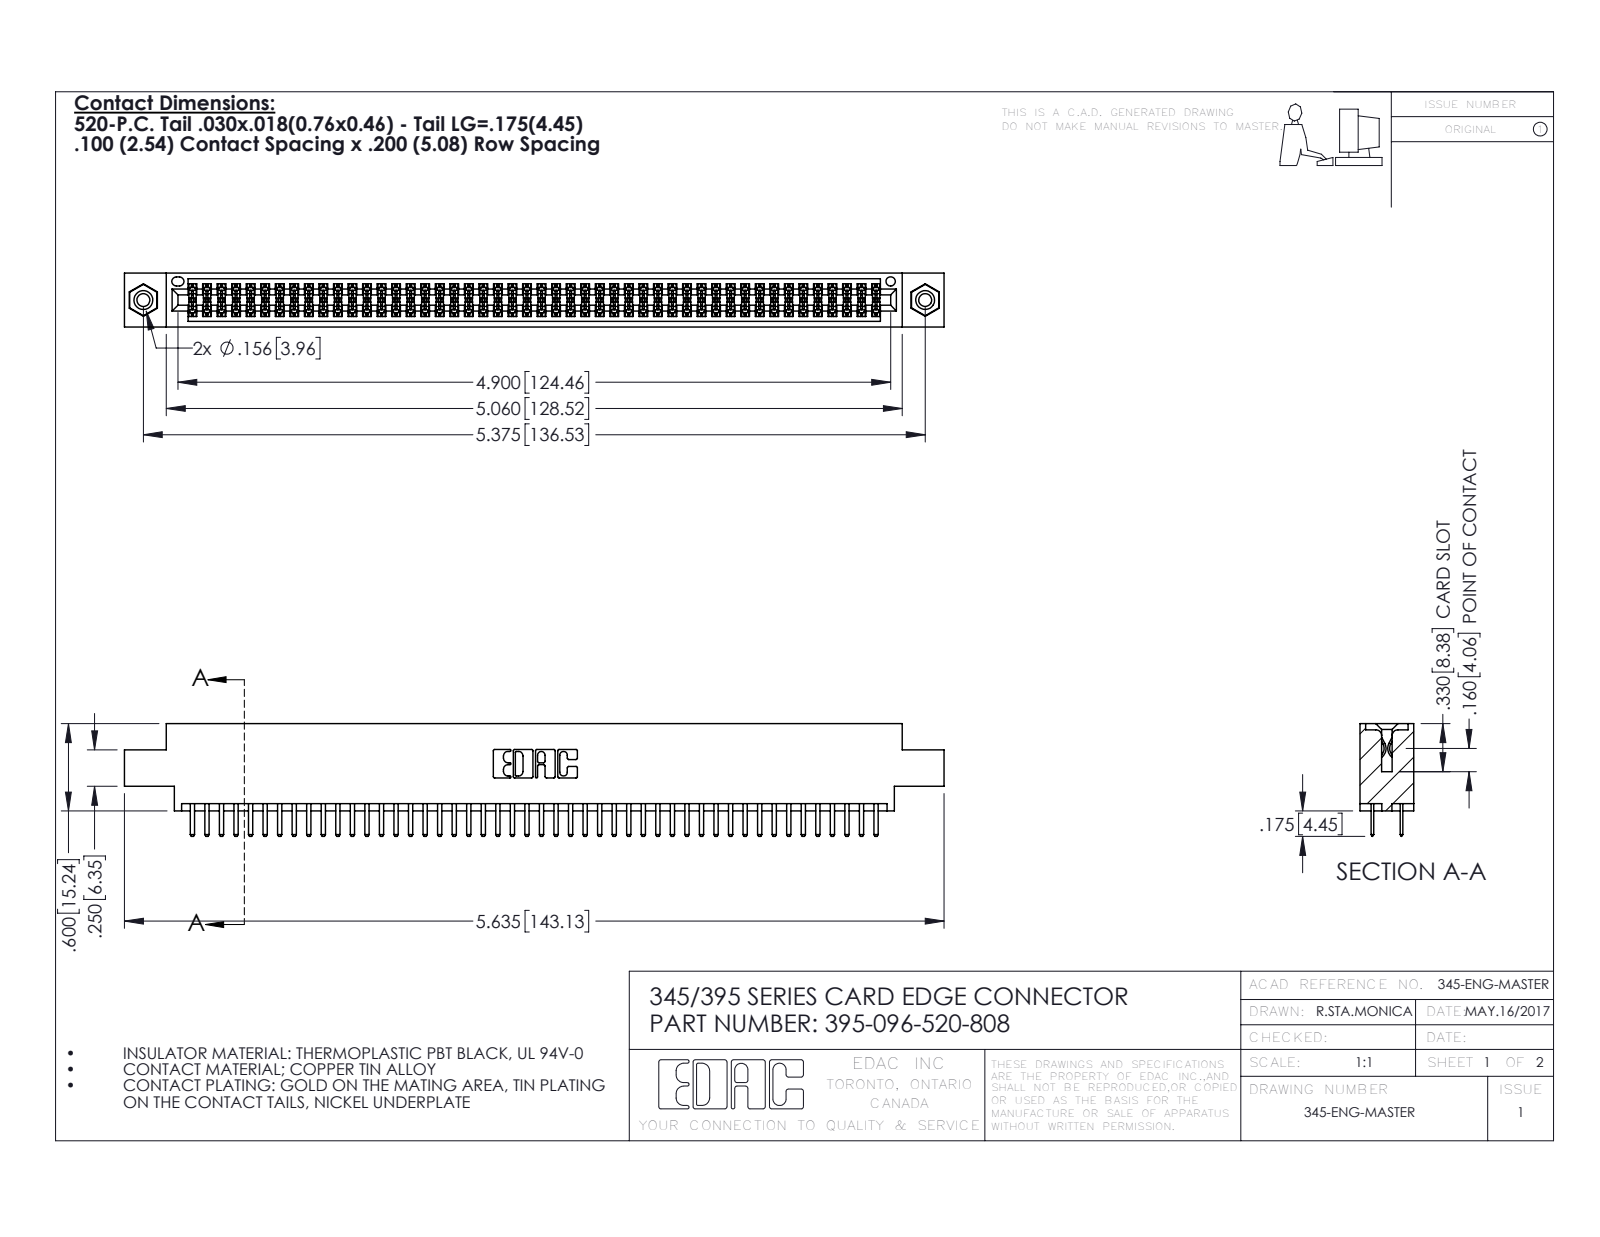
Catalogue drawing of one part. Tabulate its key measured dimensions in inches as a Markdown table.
| quantity | value |
| --- | --- |
| part name | 395-096-520-808; 345 Part_0.170 Offset - 0.156 Dia-TI; 345-292-001_345-293-120; 345-250-001_345-250-003-102 |
| STEP written by | SolidWorks 2016 (CONFIG_CONTROL_DESIGN) |
| units | inches |
| bodies | 99 solids, 5374 faces (3476 planar, 1882 cylindrical, 16 other) |
| overall size | 5.635 × 0.775 × 0.37 |
| volume | 0.842 in³ |
| surface area | 31.9 in² |
| round holes (diameter × count) | 0.089 × 2, 0.125 × 2, 0.156 × 2, 0.064 × 1 |
| round bosses / shafts (diameter × count) | 0.155 × 2 |
| partial cylindrical surfaces (radius × count) | 0.006 × 145, 0.01 × 100, 0.01 × 22, 0.007 × 6, 0.031 × 6, 0.026 × 3, 0.014 × 2, 0.019 × 2 |
| main face-to-face distances | 0.072, 0.298, 0.2, 0.37, 0.098, 0.272, 0.025, 0.225, 0.022, 0.072 |
| hole center spacings | 0.27, 5.139, 5.375 |
